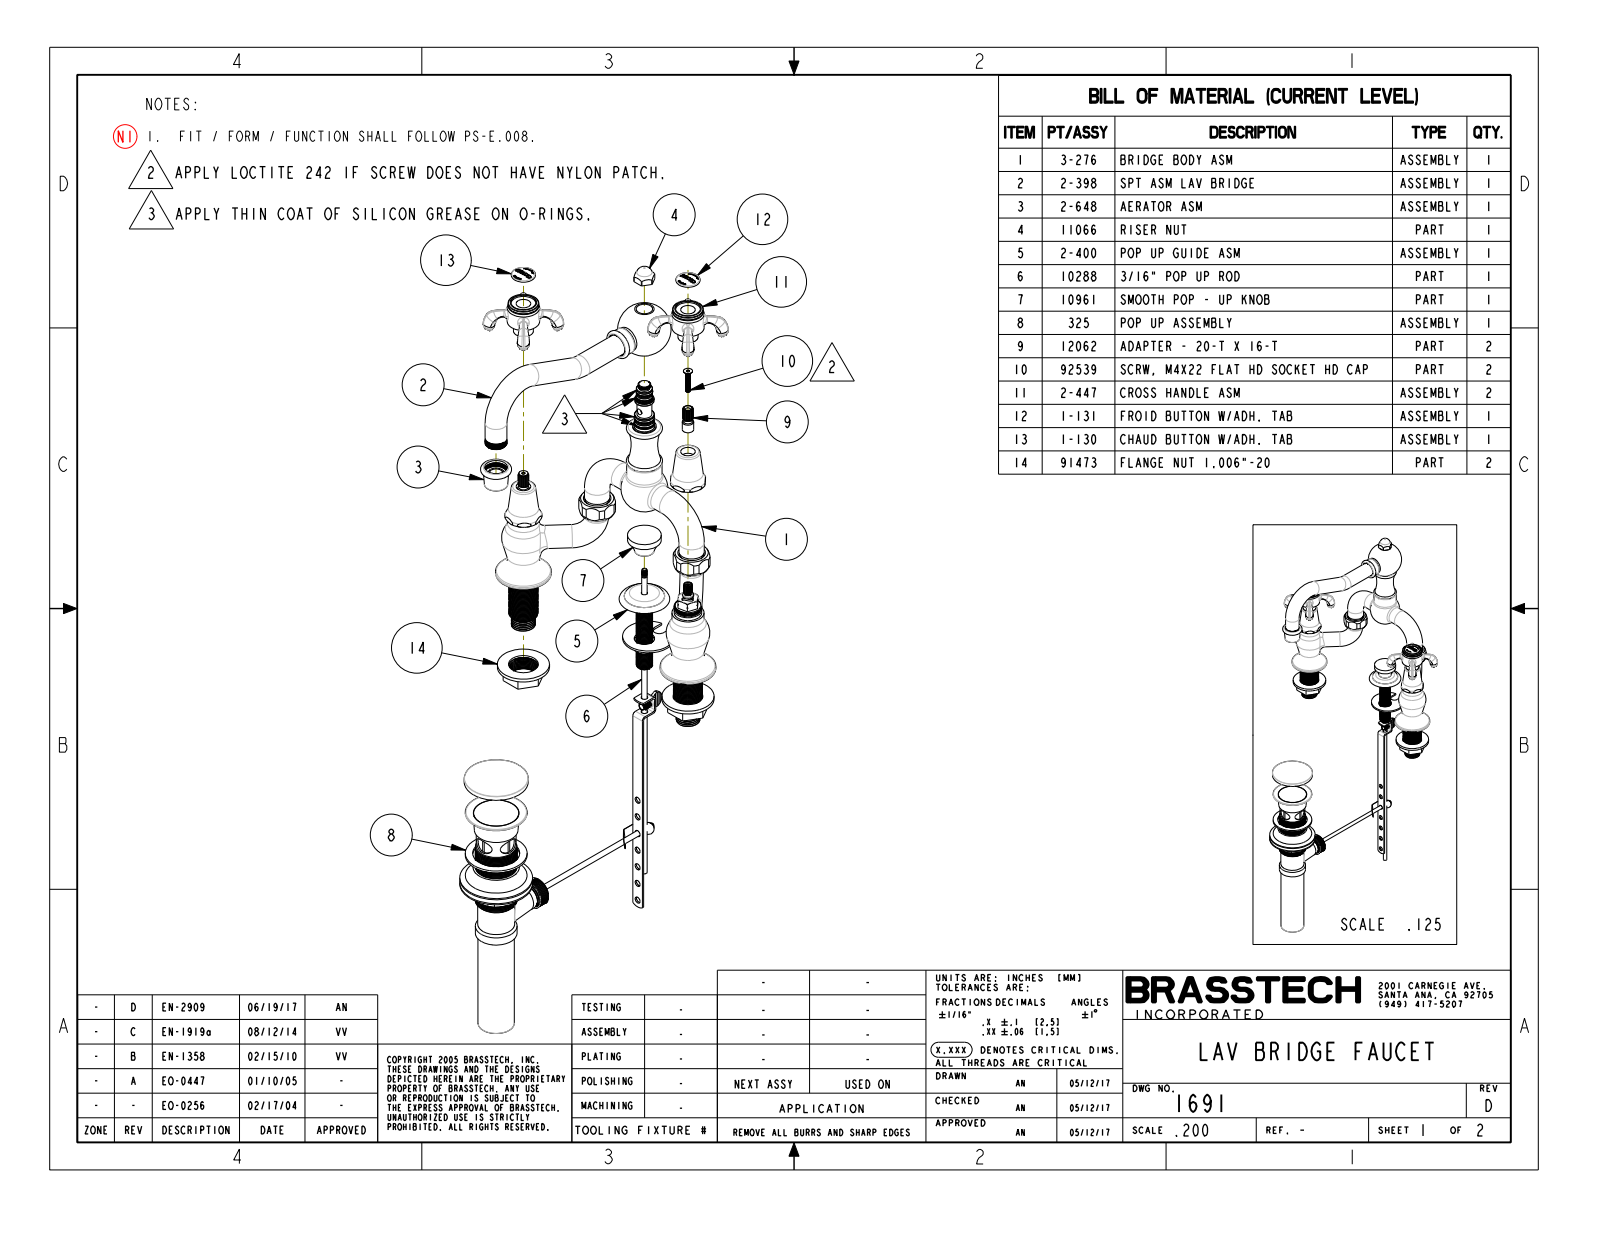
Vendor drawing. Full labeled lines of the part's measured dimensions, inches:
Part name (STEP PRODUCT): 1691_WEB
STEP written by: PRO/ENGINEER BY PARAMETRIC TECHNOLOGY CORPORATION, 2009300 (CONFIG_CONTROL_DESIGN)
Units: inches
Bodies: 0 solids, 784 faces (51 planar, 91 cylindrical, 642 other)
Overall size (bounding box): 11.711 × 9.359 × 8.766
Round bosses / shafts (diameter × count): ⌀0.874 ×3, ⌀0.75 ×3, ⌀1.917 ×2, ⌀1.115 ×2, ⌀1.102 ×2, ⌀1.055 ×2, ⌀0.807 ×2, ⌀0.687 ×2
Partial cylindrical surfaces — rounded edges, fillets, slot ends (radius × count): R0.637 ×2, R0.37 ×1
Main face-to-face distances: 2.516, 3.096, 0.58, 0.125, 2.391, 2.971, 1.188, 4.537, 4.412, 2.021
